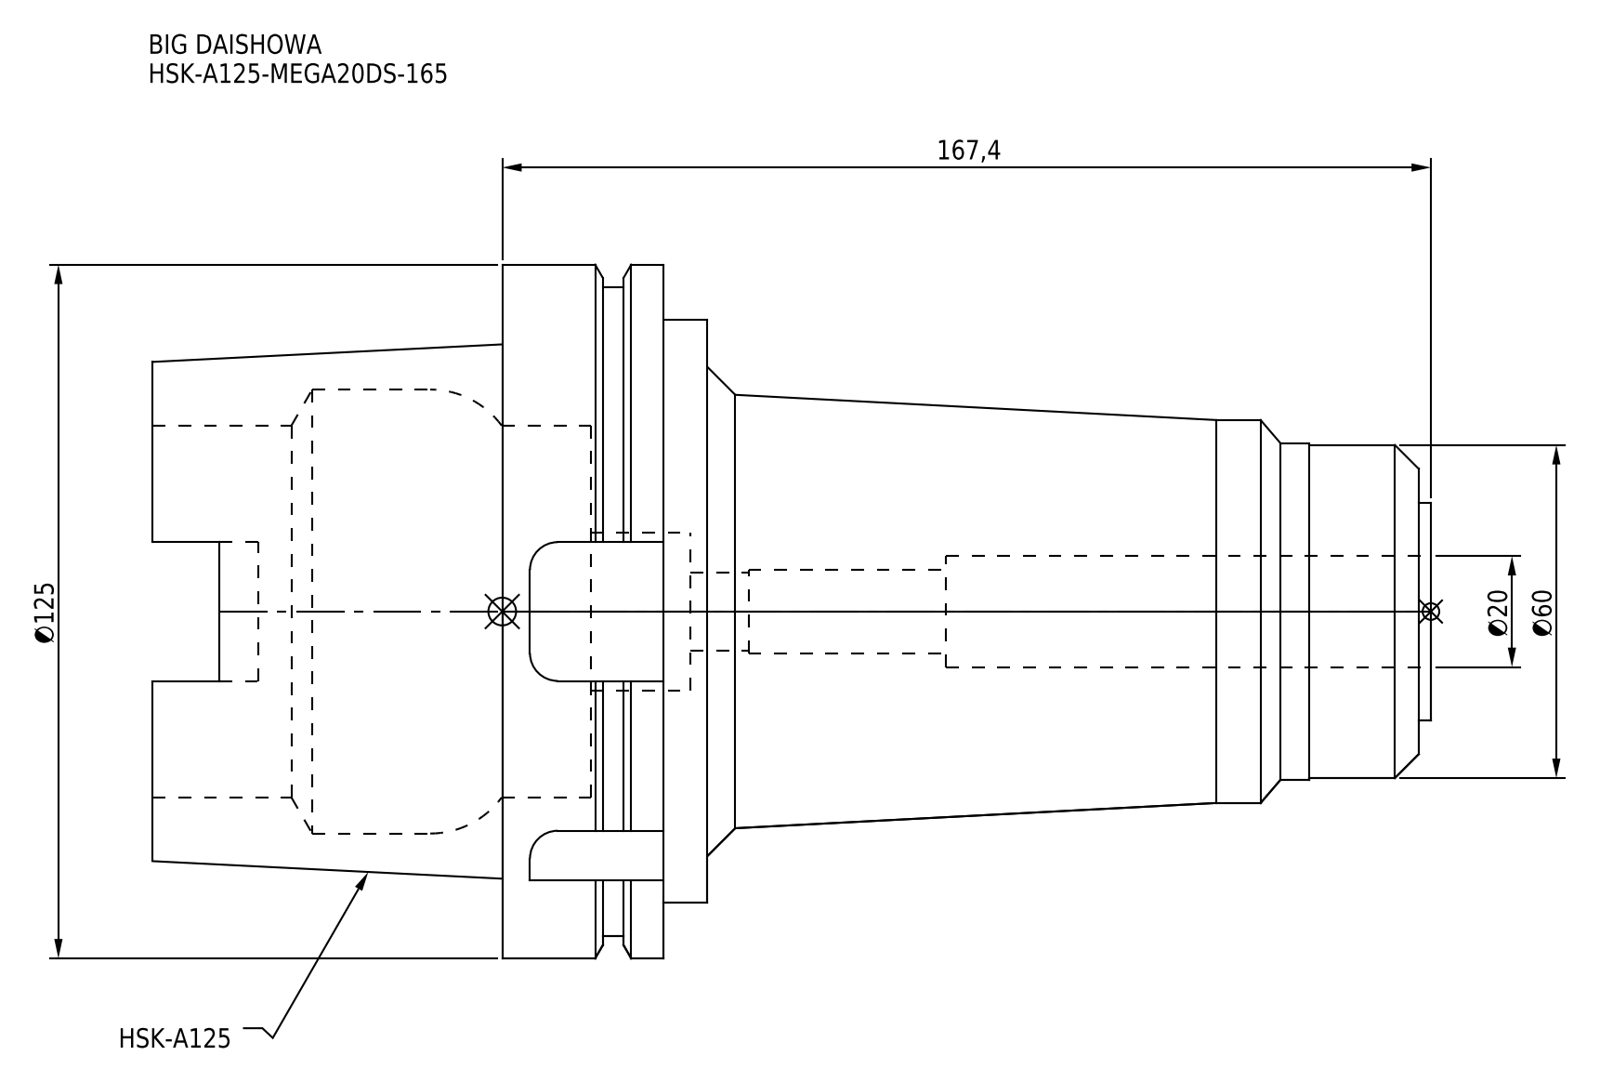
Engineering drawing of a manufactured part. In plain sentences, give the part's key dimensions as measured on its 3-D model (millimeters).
The part is named "HSK-A125-MEGA20DS-165". Its 3-D file was written by "CREO PARAMETRIC BY PTC INC, 2016380 (AUTOMOTIVE_DESIGN)". It is 1 solid with 102 faces: 39 planar, 43 cylindrical and 20 other. Overall it measures 230.4 by 125 by 125 millimeters. Its volume is 965 295 cubic millimeters and its surface area 111 545 square millimeters. Round holes: 1 of diameter 14, 1 of diameter 15, 1 of diameter 20, 1 of diameter 28.5, 1 of diameter 67, 1 of diameter 80. Round bosses or shafts: 1 of diameter 125, 1 of diameter 117, 1 of diameter 105, 1 of diameter 69, 1 of diameter 60.7, 1 of diameter 60, 1 of diameter 39.3. Partial cylindrical surfaces (rounded edges, fillets, slot ends): 5 of radius 5, 4 of radius 5.88. The main face-to-face distances are 29, 13.05, 15.95, 8, 21.05, 37, 100, 92, 78.95, 63.
